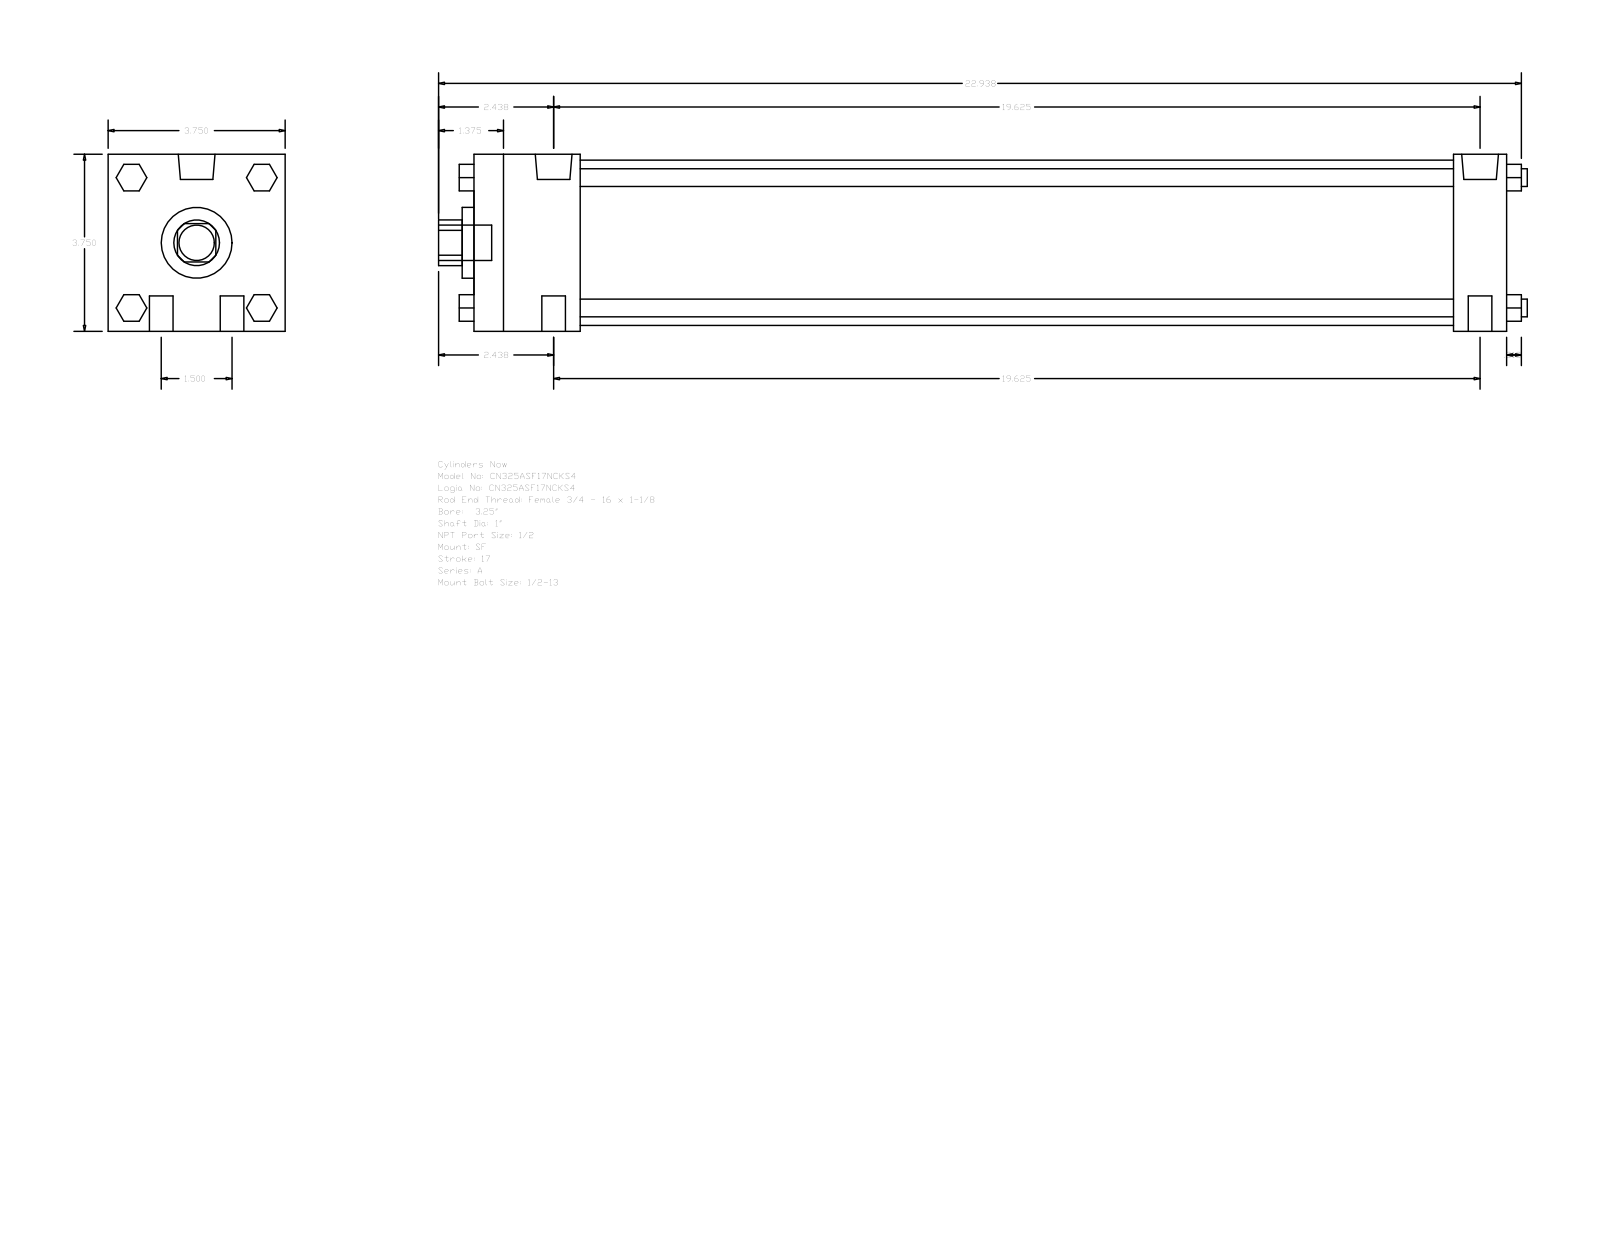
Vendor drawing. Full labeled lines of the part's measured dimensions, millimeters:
Part name (STEP PRODUCT): A_SF__0325_1
STEP written by: GSSL Pune (CONFIG_CONTROL_DESIGN)
Units: millimetres
Bodies: 0 solids, 124 faces (94 planar, 30 cylindrical, 0 other)
Overall size (bounding box): 585.79 × 95.25 × 95.25
Round holes (diameter × count): ⌀25.4 ×1, ⌀38.1 ×1, ⌀88.9 ×1
Round bosses / shafts (diameter × count): ⌀12.7 ×4, ⌀9.53 ×4, ⌀19.77 ×2, ⌀8.73 ×2, ⌀19.05 ×1
Partial cylindrical surfaces — rounded edges, fillets, slot ends (radius × count): R12.29 ×1
Main face-to-face distances: 95.24, 555.62, 28.57, 527.05, 57.15, 469.9, 498.47, 14.28, 35.05, 60.71
